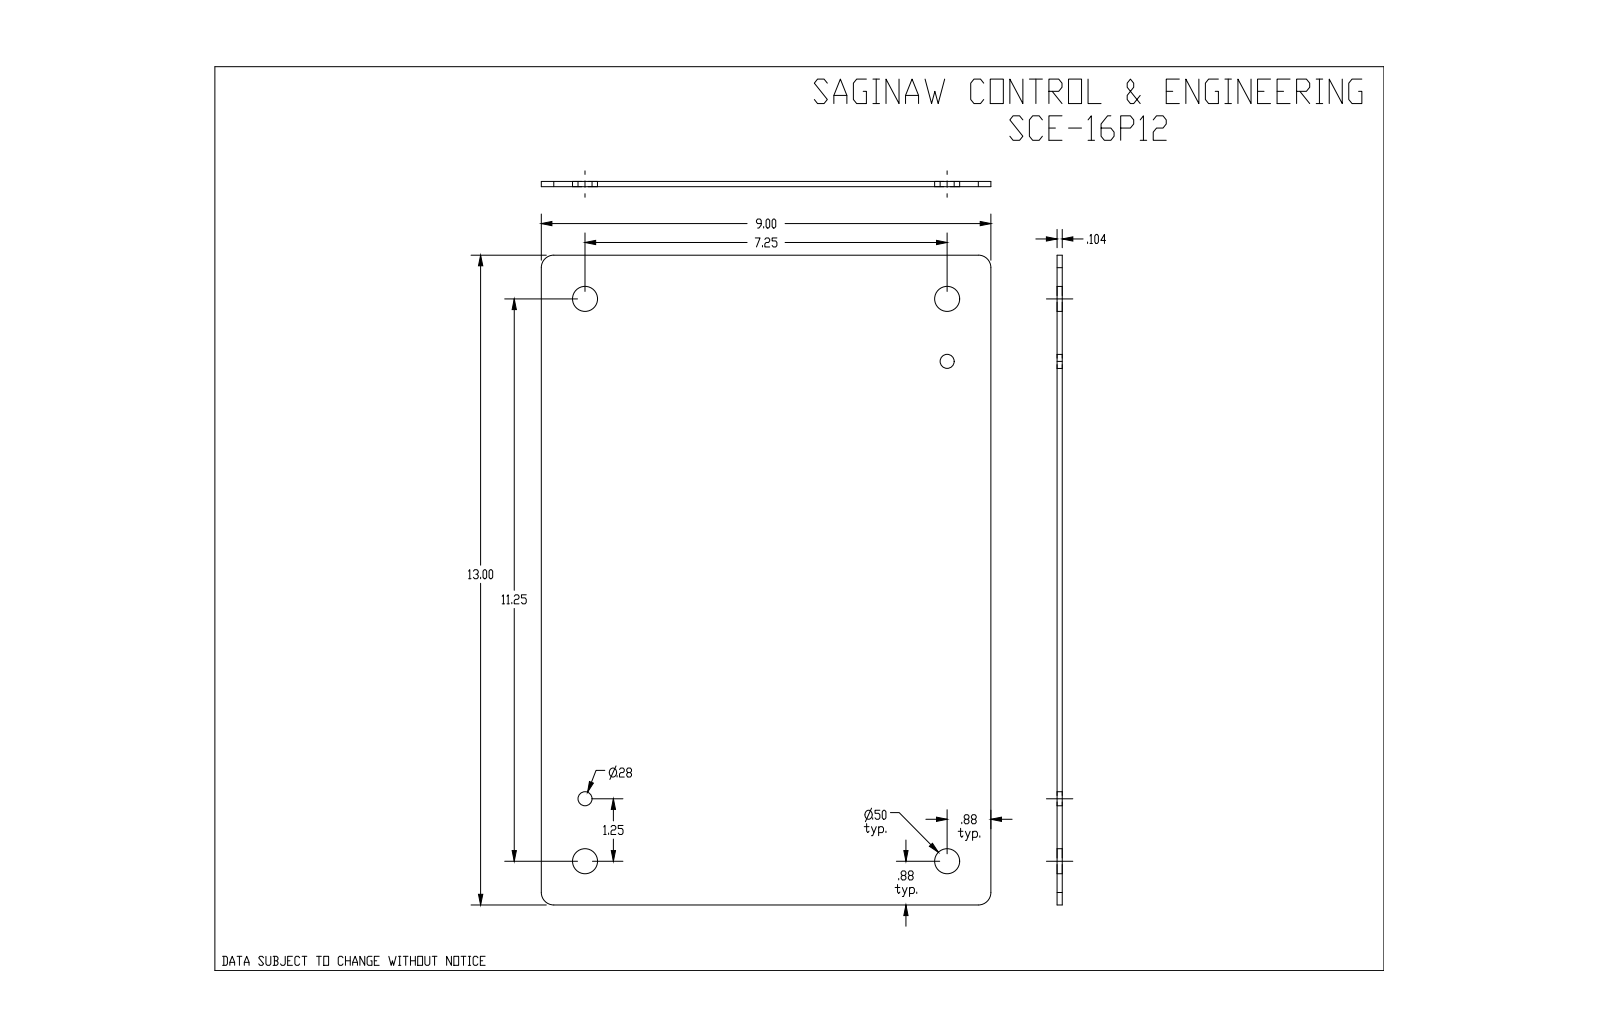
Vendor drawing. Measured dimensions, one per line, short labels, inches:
name: SCE-16P12
written by: SolidWorks 2019 (CONFIG_CONTROL_DESIGN)
unit: in
bodies: 1 solid, 16 faces (6 planar, 10 cylindrical, 0 other)
size: 13 × 9 × 0.104
volume: 12.07 in³; area: 237.4 in²
holes: 4× ⌀0.5, 1× ⌀0.281, 1× ⌀0.281
rounds: 4× R0.25
face distances: 0.104, 9, 13
hole spacings: 1.25, 7.25, 7.357, 10, 11.25, 12.352, 13.384, 11.363
